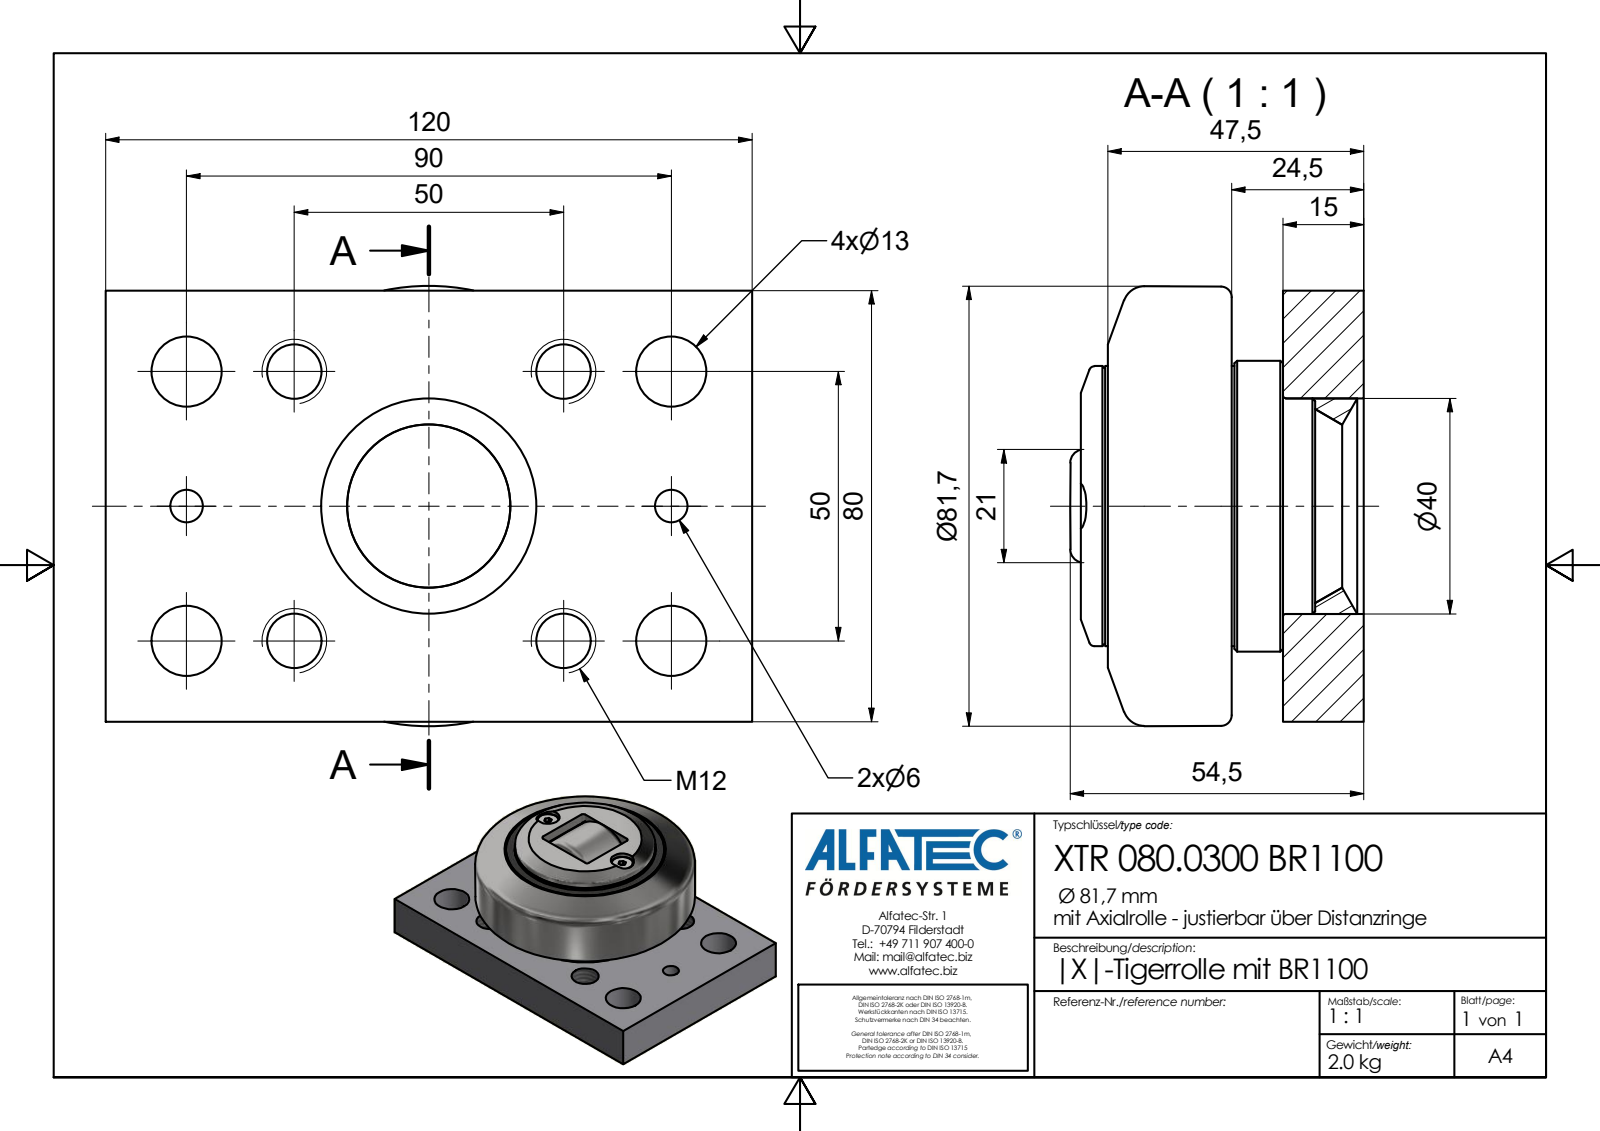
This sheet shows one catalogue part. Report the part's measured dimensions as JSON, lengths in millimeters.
{"part_name": "XTR 080.0300 BR1100_Kontur", "step_written_by": "Autodesk Inventor 2020 (AP242_MANAGED_MODEL_BASED_3D_ENGINEERING_MIM_LF)", "units": "millimeters", "bodies": {"solids": 1, "faces": 105, "planar": 46, "cylindrical": 38, "other": 21}, "overall_size": [120, 81.7, 54.5], "volume_mm3": 271796, "surface_area_mm2": 44549, "round_holes": [[10.11, 4], [13, 4], [4.5, 2], [6, 2], [8.6, 2], [40, 1], [46.2, 1]], "round_bosses_or_shafts": [[7.8, 2], [4, 2], [54, 1], [52, 1], [32.8, 1]], "partial_cylinders_radius": [[1, 4], [8, 1], [9, 1], [10.5, 1]], "face_to_face_distances": [15, 24.5, 9.5, 80, 120, 48, 0.5, 23.5, 47.5, 32.5], "hole_center_spacings": [50, 20, 25, 25.6, 32.02, 35.36, 35.71, 51.04]}
